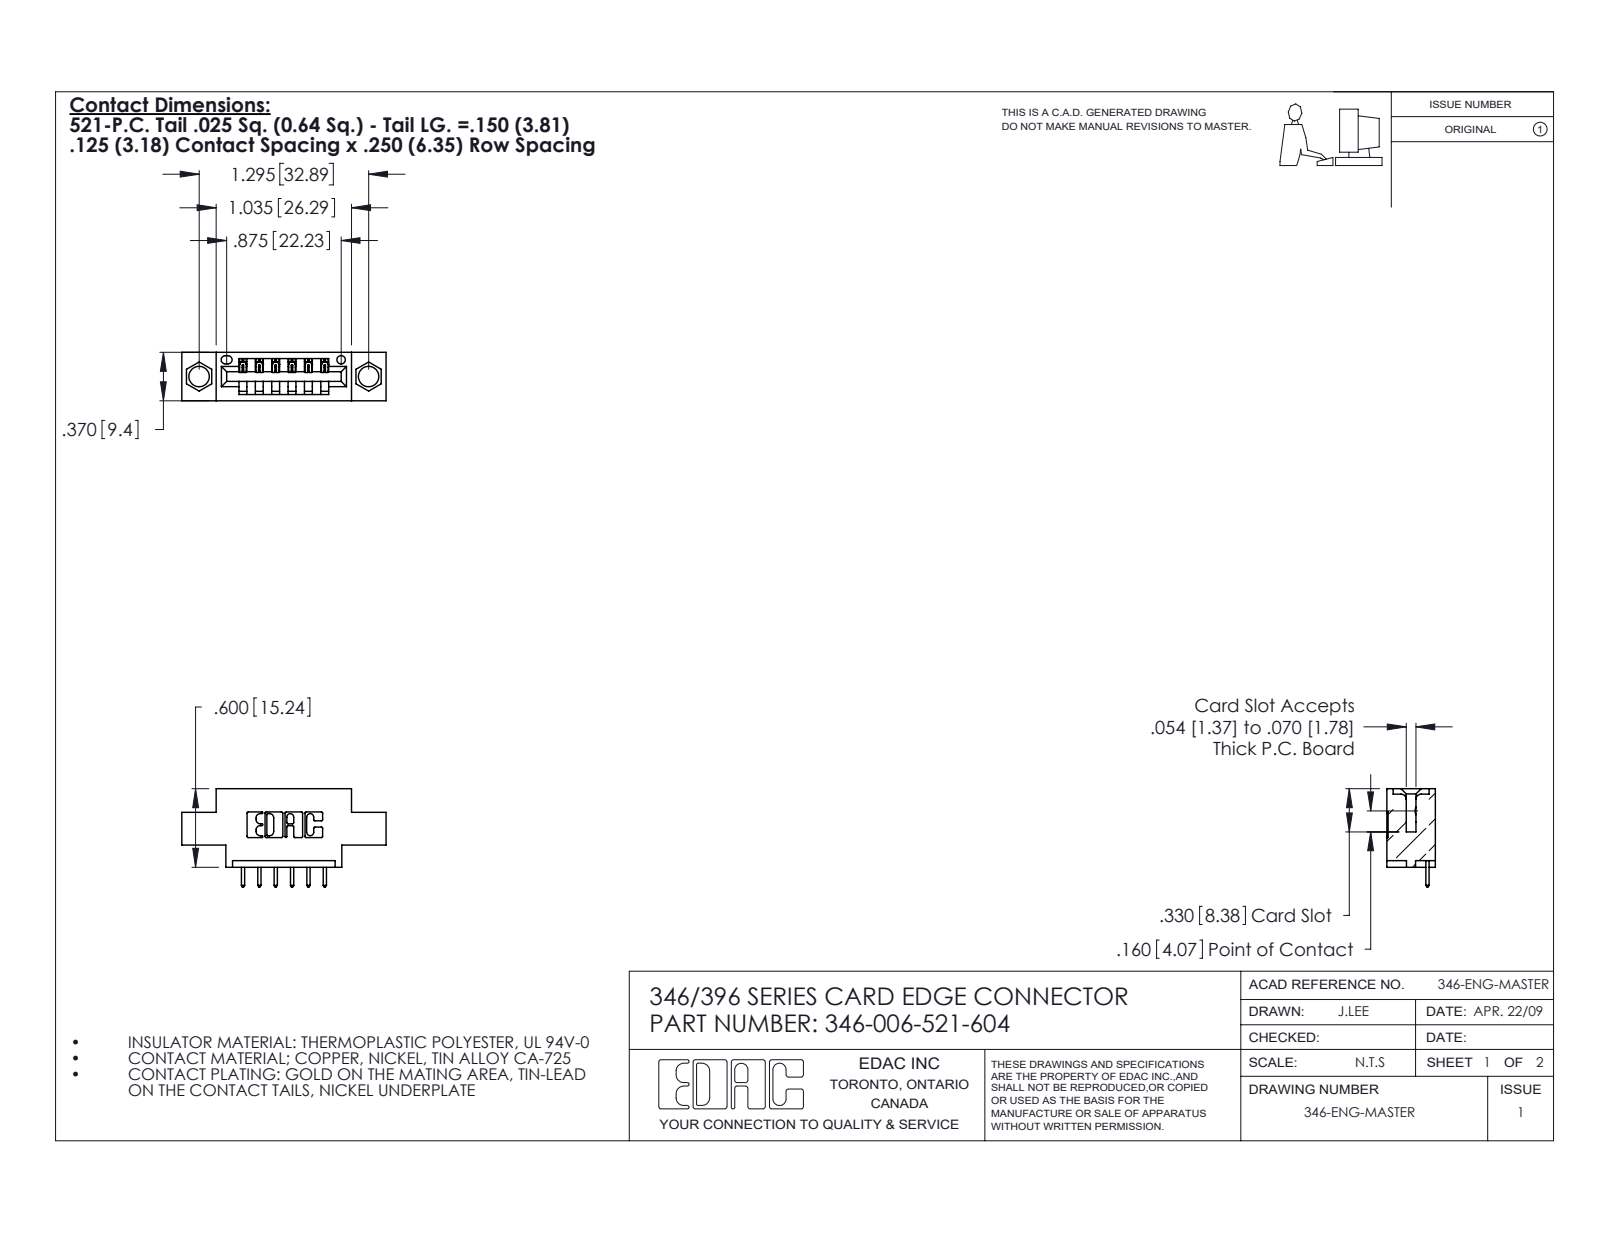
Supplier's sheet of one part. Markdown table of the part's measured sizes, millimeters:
| quantity | value |
| --- | --- |
| part name | 346 Part_0.170 Offset - 0.156 Dia-TH; 345-292-001_345-293-121; 346-006-521-604 |
| STEP written by | SolidWorks 2020 (CONFIG_CONTROL_DESIGN) |
| units | millimeters |
| bodies | 7 solids, 488 faces (334 planar, 154 cylindrical, 0 other) |
| overall size | 39.6 × 19.1 × 9.4 |
| volume | 3 260 mm³ |
| surface area | 3 625 mm² |
| round holes (diameter × count) | 4 × 2, 1.6 × 1 |
| partial cylindrical surfaces (radius × count) | 0.3 × 22, 0.2 × 12, 0.3 × 12, 0.2 × 6, 0.8 × 6, 0.7 × 3, 0.8 × 2, 1 × 2 |
| main face-to-face distances | 6.4, 9.4, 1.2, 8.2, 5.6, 3.8, 2.5, 4.4, 3.2, 4.7 |
| hole center spacings | 6.2, 27.7, 32.9 |
